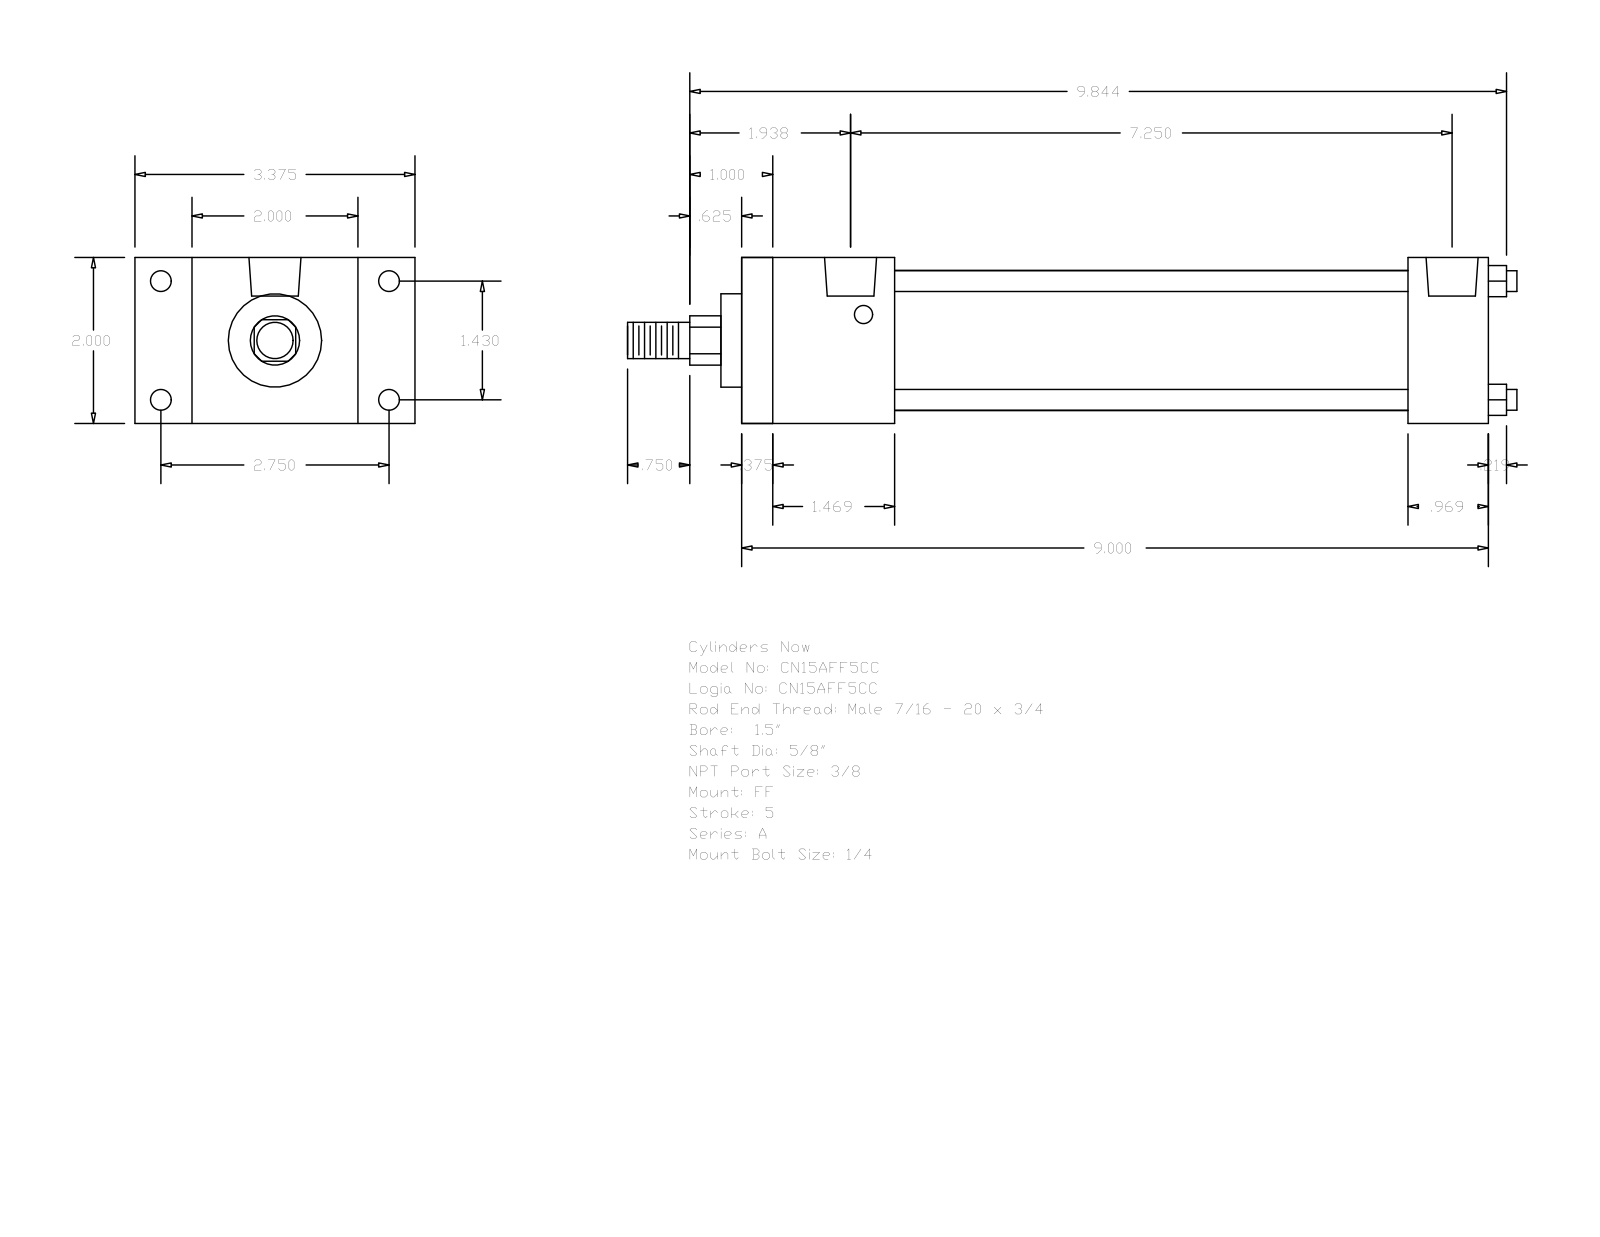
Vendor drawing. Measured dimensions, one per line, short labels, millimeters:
name: A_FF__0150_0.625
written by: GSSL Pune (CONFIG_CONTROL_DESIGN)
unit: mm
bodies: 0 solids, 92 faces (64 planar, 28 cylindrical, 0 other)
size: 272.26 × 85.72 × 50.8
holes: 4× ⌀5.56, 4× ⌀6.35, 2× ⌀15.93
bosses: 4× ⌀6.35, 1× ⌀42.93, 1× ⌀28.57, 1× ⌀15.88, 1× ⌀11.11
rounds: 1× R7.54
face distances: 50.8, 228.59, 9.52, 219.07, 46.83, 203.99, 37.31, 194.47, 157.16, 181.76
hole spacings: 3.97, 36.32, 69.84, 78.72, 176.21, 180.18, 184.15
